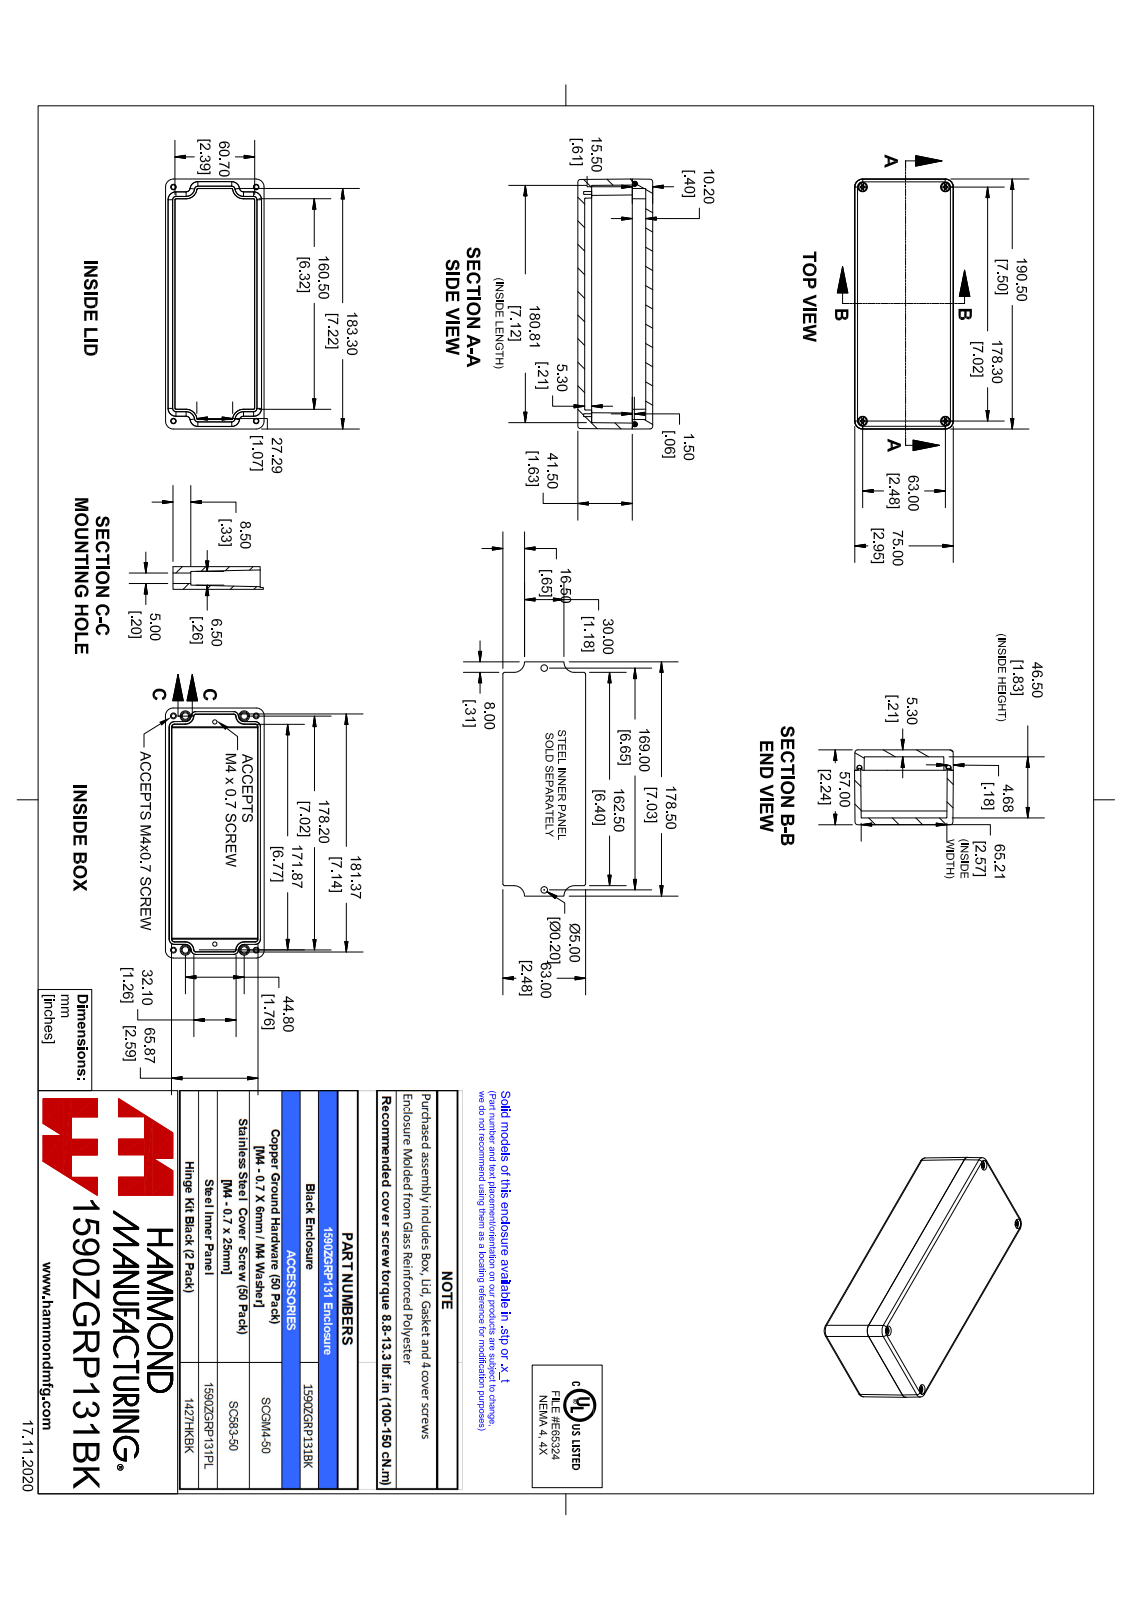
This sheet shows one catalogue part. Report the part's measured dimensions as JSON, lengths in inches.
{"part_name": "1590ZGRP131BK", "step_written_by": "SolidWorks 2021 (AUTOMOTIVE_DESIGN)", "units": "inches", "bodies": {"solids": 8, "faces": 402, "planar": 221, "cylindrical": 71, "other": 110}, "overall_size": [7.5, 2.961, 2.185], "volume_in3": 15.46, "surface_area_in2": 226.2, "round_holes": [[0.128, 6], [0.197, 6], [0.138, 4], [0.177, 4], [0.283, 4]], "round_bosses_or_shafts": [[0.148, 6], [0.354, 4], [0.272, 4], [0.152, 4], [0.137, 4]], "partial_cylinders_radius": [[0.079, 8], [0.236, 8], [0.315, 4], [0.02, 2], [0.068, 1]], "face_to_face_distances": [2.165, 0.184, 0.374, 1.791, 0.394, 0.02, 0.138, 1.772, 2.028, 0.236], "hole_center_spacings": [0.358, 2.122, 2.48, 0.899, 1.253, 1.253, 6.897, 6.954]}
